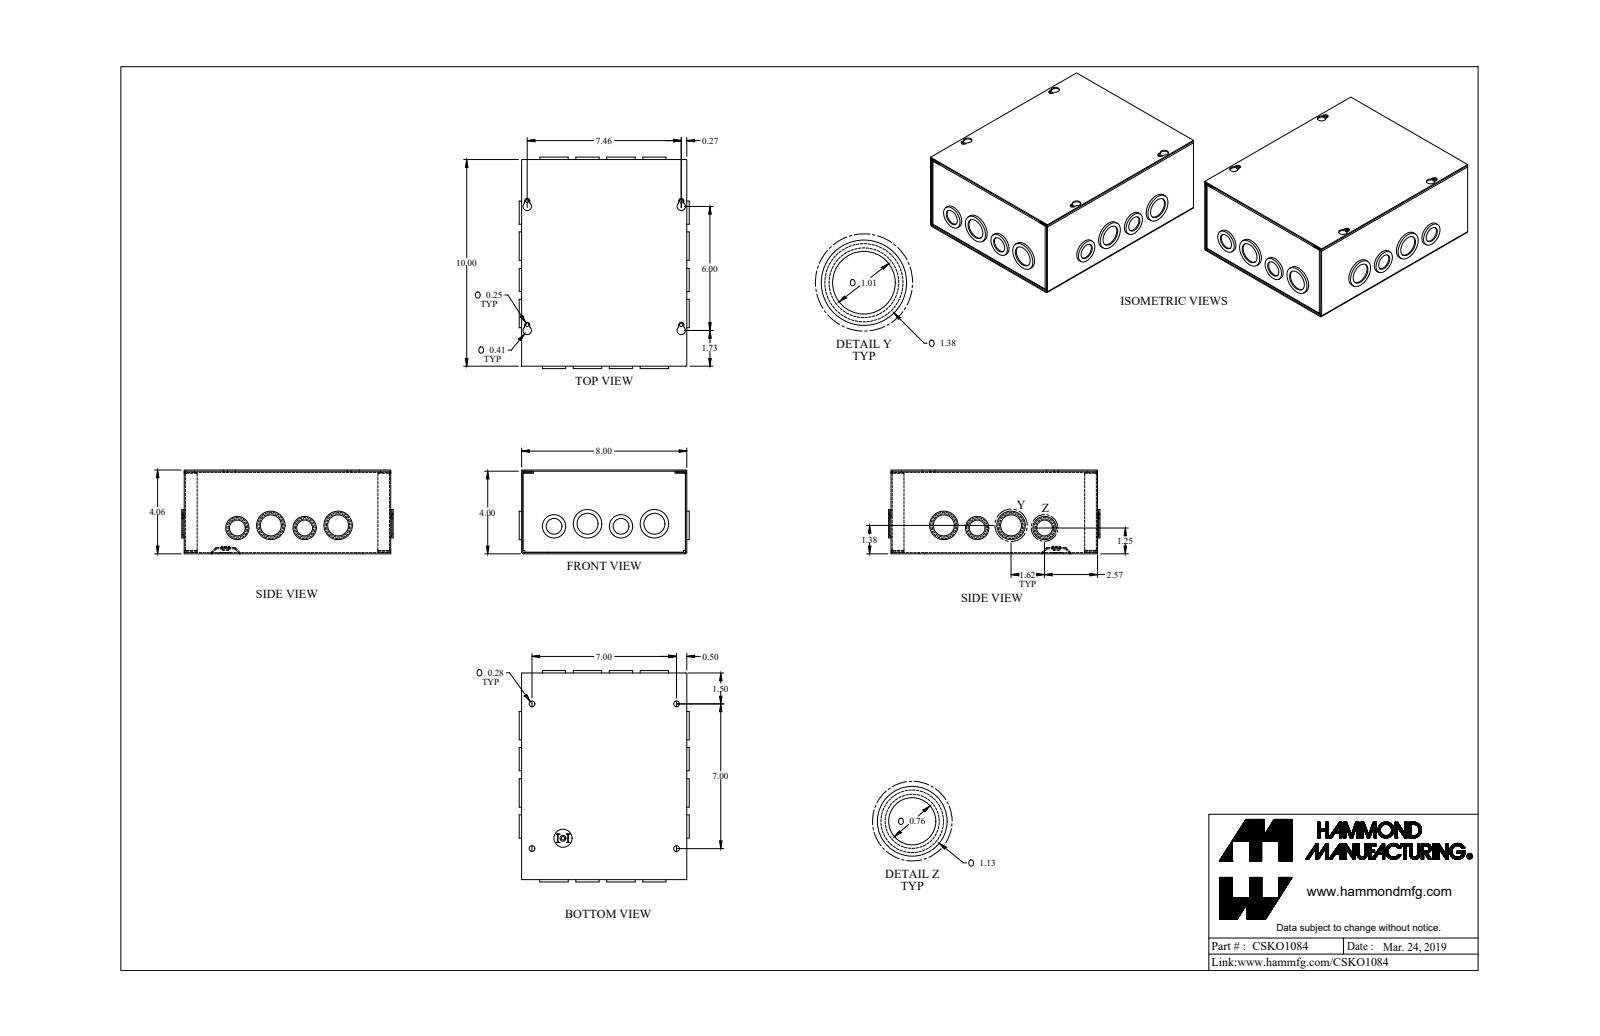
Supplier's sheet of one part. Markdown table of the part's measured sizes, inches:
| quantity | value |
| --- | --- |
| part name | CSKO1084_Default |
| STEP written by | SolidWorks 2019 (CONFIG_CONTROL_DESIGN) |
| units | inches |
| bodies | 4 solids, 397 faces (189 planar, 200 cylindrical, 8 other) |
| overall size | 10.234 × 8.234 × 4.057 |
| volume | 19.36 in³ |
| surface area | 688.2 in² |
| round holes (diameter × count) | 1.011 × 12, 0.761 × 6, 1.261 × 6, 0.17 × 5, 0.281 × 4, 0.5 × 1 |
| round bosses / shafts (diameter × count) | 1.125 × 7, 0.875 × 6, 1.375 × 5, 1.125 × 5, 0.875 × 2, 1.375 × 1, 0.492 × 1, 0.284 × 1 |
| partial cylindrical surfaces (radius × count) | 0.029 × 12, 0.086 × 12, 0.057 × 8, 0.125 × 4, 0.203 × 4 |
| main face-to-face distances | 0.057, 4, 3.943, 4.057, 7.943, 9.943, 8, 7.886, 10, 9.886 |
| hole center spacings | 1.625, 0.125, 0.55, 1.62, 3.24, 3.242, 6.504, 7 |
